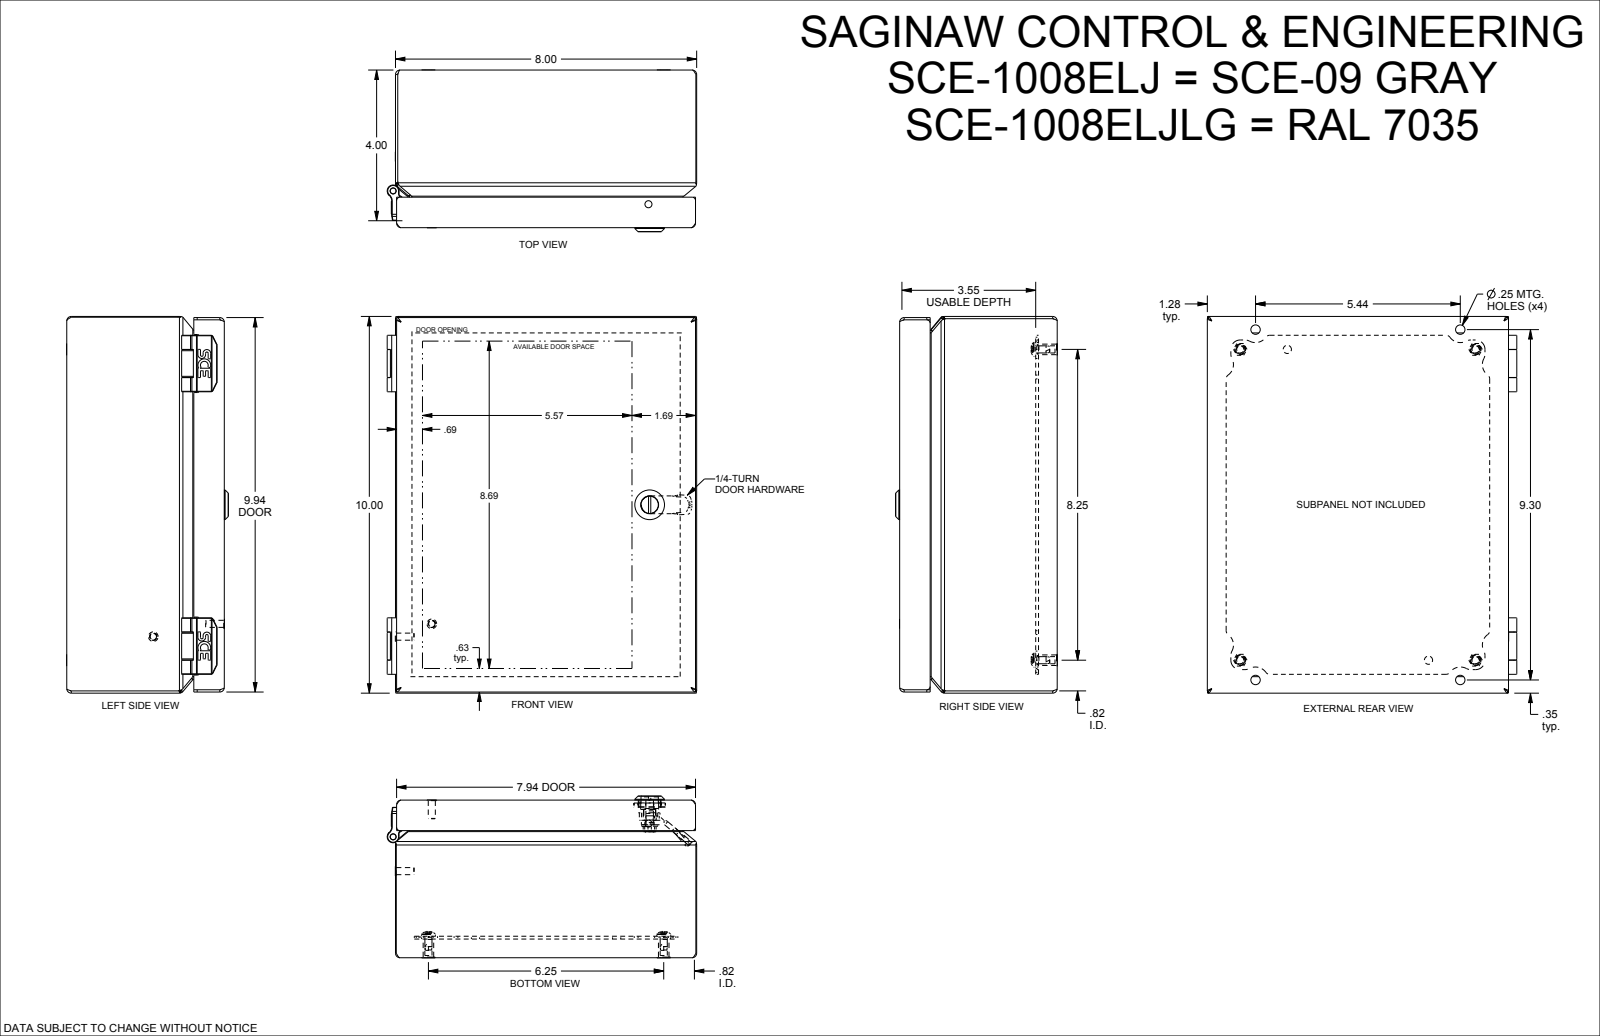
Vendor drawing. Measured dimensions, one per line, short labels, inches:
name: SCE-1008ELJ
written by: SolidWorks 2019 (AUTOMOTIVE_DESIGN)
unit: in
bodies: 30 solids, 947 faces (362 planar, 317 cylindrical, 268 other)
size: 9.999 × 8.22 × 4.296
volume: 27.32 in³; area: 848.7 in²
holes: 4× ⌀0.19, 4× ⌀0.25, 4× ⌀0.284, 2× ⌀0.02, 2× ⌀0.1, 2× ⌀0.218, 2× ⌀0.266, 1× ⌀0.158, 1× ⌀0.196, 1× ⌀0.2, 1× ⌀0.239, 1× ⌀0.254
bosses: 6× ⌀0.188, 4× ⌀0.373, 4× ⌀0.28, 4× ⌀0.16, 2× ⌀0.26, 2× ⌀0.256, 2× ⌀0.237, 2× ⌀0.23
rounds: 28× R0.03, 21× R0.013, 16× R0.05, 13× R0.25, 11× R0.125, 10× R0.01, 10× R0.06, 8× R0.344
face distances: 0.059, 0.06, 4.131, 4.072, 4.191, 4.131, 0.5, 0.441, 0.575, 0.516
hole spacings: 1.25, 4.142, 5, 6.25, 7.18, 7.5, 8.25, 8.344
